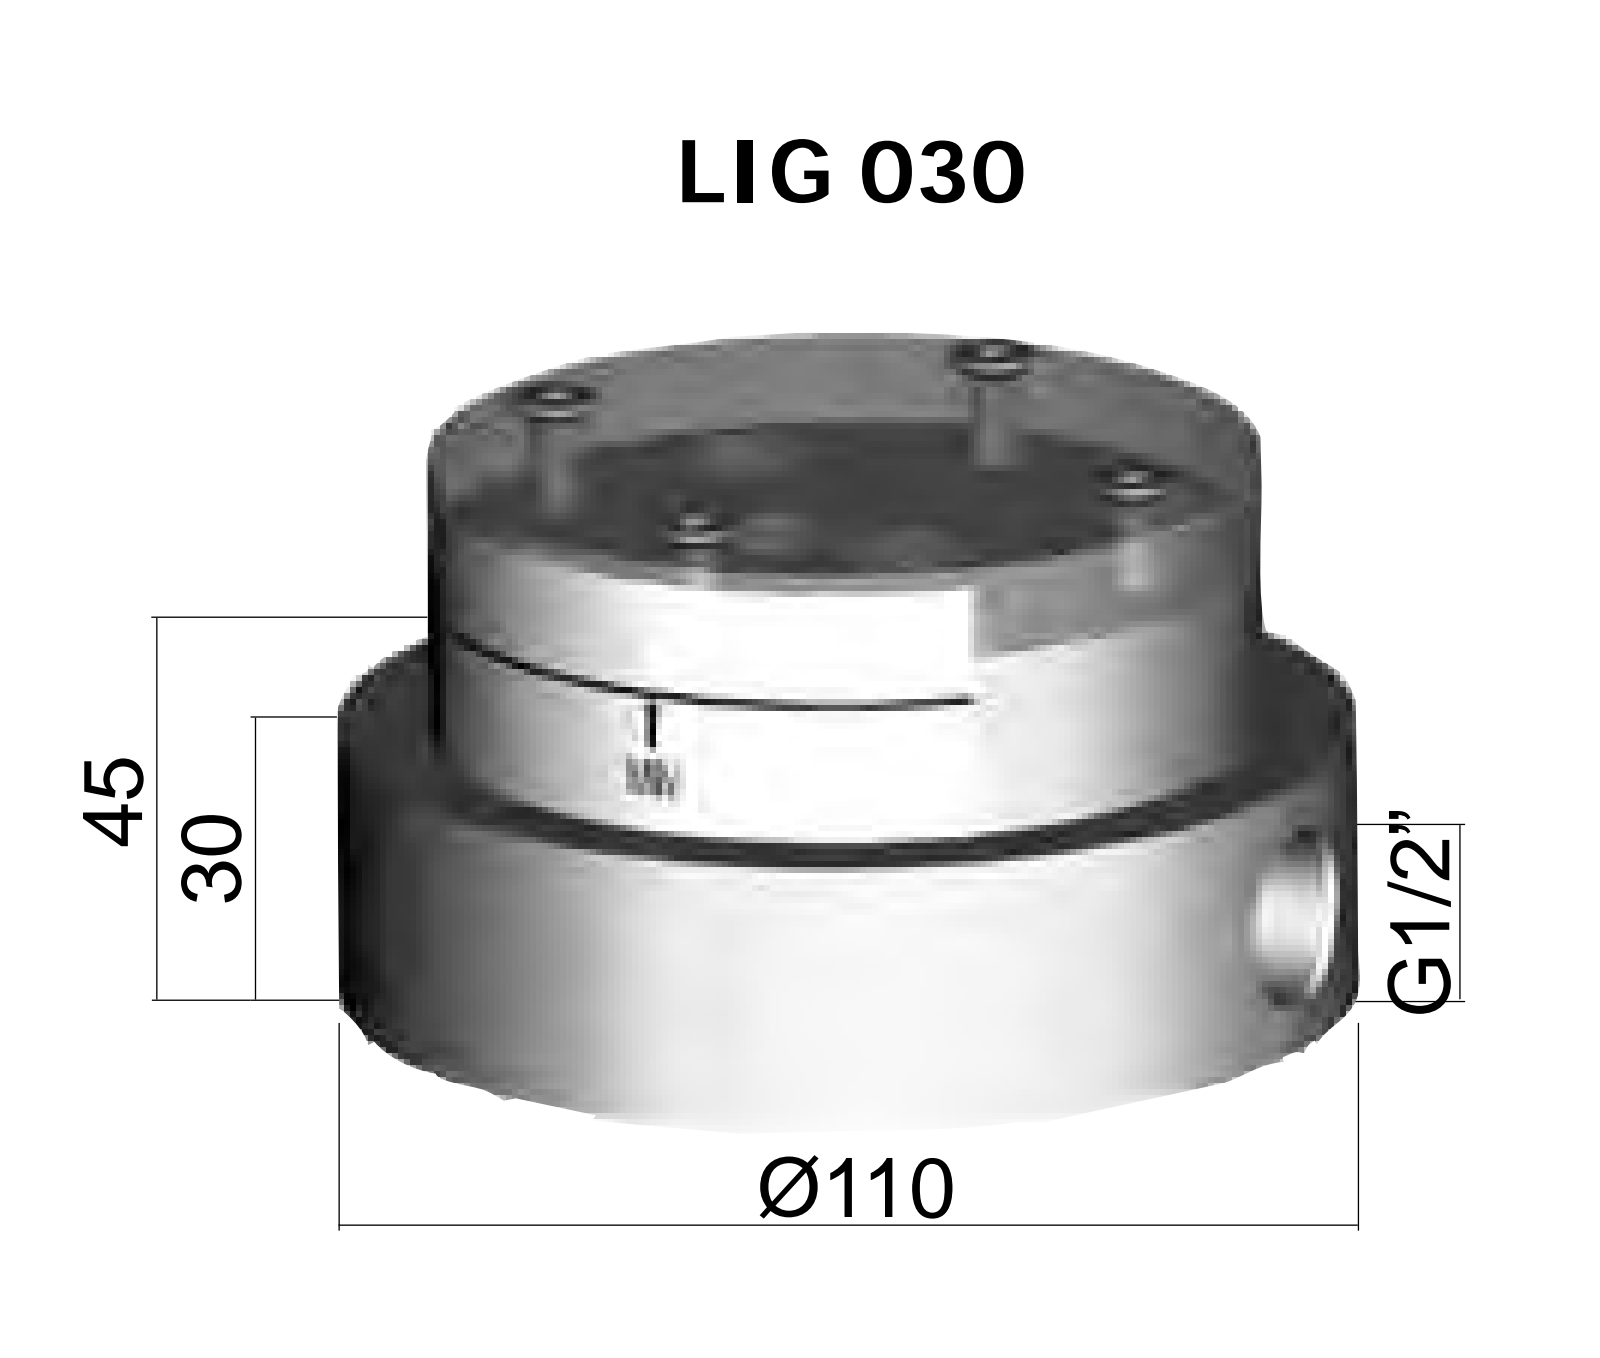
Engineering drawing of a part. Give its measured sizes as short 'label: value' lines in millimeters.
name: LIG030
written by: CREO PARAMETRIC BY PTC INC, 2020044 (CONFIG_CONTROL_DESIGN)
unit: mm
bodies: 1 solid, 201 faces (87 planar, 78 cylindrical, 36 other)
size: 110 × 110 × 62.5
volume: 423 619 mm³; area: 66 073 mm²
holes: 4× ⌀6, 4× ⌀6.5, 4× ⌀15, 3× ⌀10, 2× ⌀8.5, 1× ⌀18.6, 1× ⌀24
bosses: 4× ⌀5, 2× ⌀15, 1× ⌀110, 1× ⌀90
rounds: 16× R0.5
face distances: 60.1, 10, 50.1, 50, 10.1, 30, 20, 20.1, 30.1, 5
hole spacings: 26.79, 49.5, 64.67, 29.89, 35.9, 41.05, 70, 27
